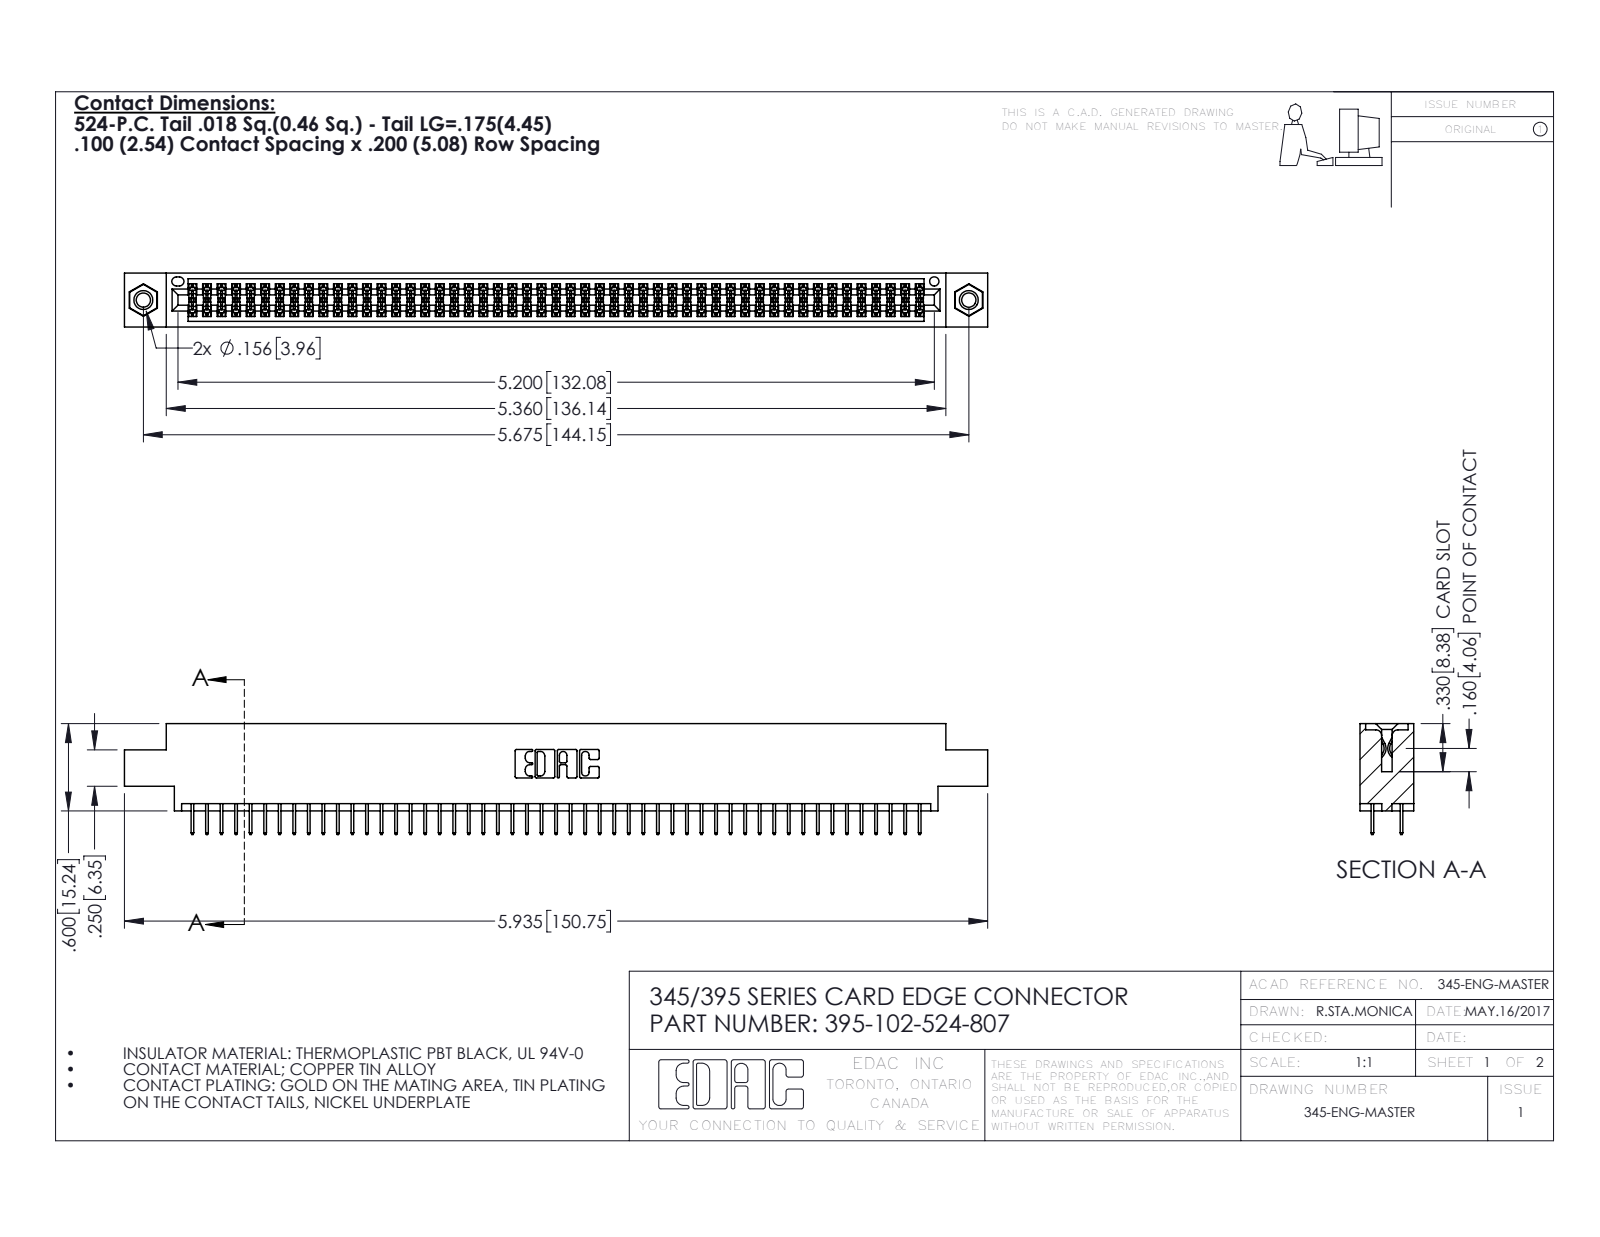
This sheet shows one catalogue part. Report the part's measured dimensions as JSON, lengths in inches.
{"part_name": "345-250-001_345-250-005-103; 395-102-524-807; 345 Part_0.170 Offset - 0.156 Dia-TI; 345-292-001_345-293-124", "step_written_by": "SolidWorks 2016 (CONFIG_CONTROL_DESIGN)", "units": "inches", "bodies": {"solids": 105, "faces": 5698, "planar": 4094, "cylindrical": 1588, "other": 16}, "overall_size": [5.935, 0.762, 0.37], "volume_in3": 0.882, "surface_area_in2": 33, "round_holes": [[0.098, 2], [0.125, 2], [0.156, 2], [0.064, 1]], "round_bosses_or_shafts": [[0.155, 2]], "partial_cylinders_radius": [[0.006, 153], [0.01, 22], [0.007, 6], [0.031, 6], [0.026, 3], [0.014, 2], [0.019, 2], [0.022, 2]], "face_to_face_distances": [0.072, 0.298, 0.37, 0.2, 0.098, 0.272, 0.025, 0.225, 0.072, 0.175], "hole_center_spacings": [0.27, 5.439, 5.675]}
